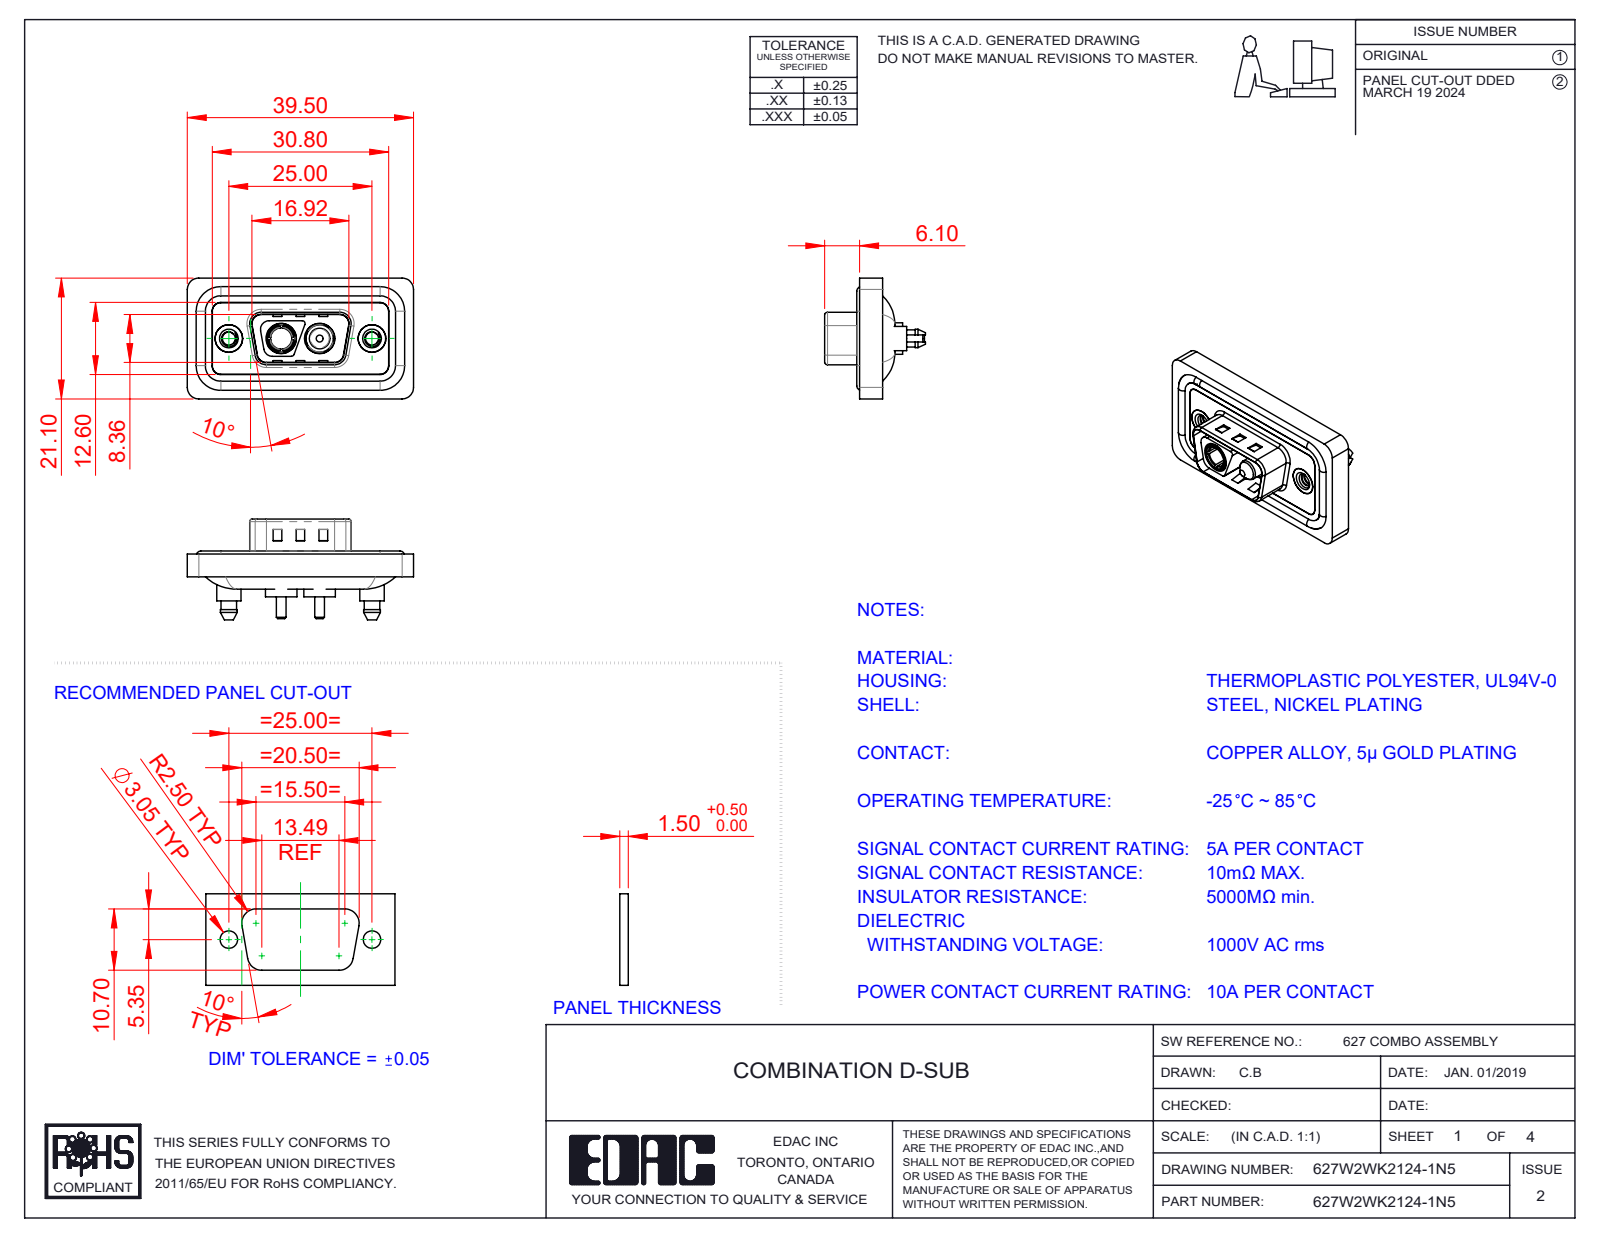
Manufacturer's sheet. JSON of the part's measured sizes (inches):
{"part_name": "627Combo Shell Front_09 Contacts; 627Combo Housing_2WK2; Power Socket_10A S; 627Combo Shell Rear_09 Contacts (+4 more)", "step_written_by": "SolidWorks 2023 (CONFIG_CONTROL_DESIGN)", "units": "inches", "bodies": {"solids": 11, "faces": 584, "planar": 205, "cylindrical": 259, "other": 120}, "overall_size": [1.555, 0.831, 0.693], "volume_in3": 0.284, "surface_area_in2": 11.86, "round_holes": [[0.089, 2], [0.157, 2], [0.189, 2], [0.191, 2], [0.197, 2], [0.209, 2], [0.146, 1]], "round_bosses_or_shafts": [[0.063, 4], [0.217, 2], [0.213, 2], [0.205, 2], [0.193, 2], [0.187, 2], [0.167, 2], [0.148, 2]], "partial_cylinders_radius": [[0.059, 26], [0.079, 18], [0.02, 10], [0.063, 10], [0.01, 4], [0.024, 4], [0.026, 4], [0.035, 4]], "face_to_face_distances": [0.016, 0.043, 0.114, 0.02, 0.063, 0.122, 0.059, 0.157, 0.071, 0.126], "hole_center_spacings": [0.36, 0.624, 0.265, 0.984]}
